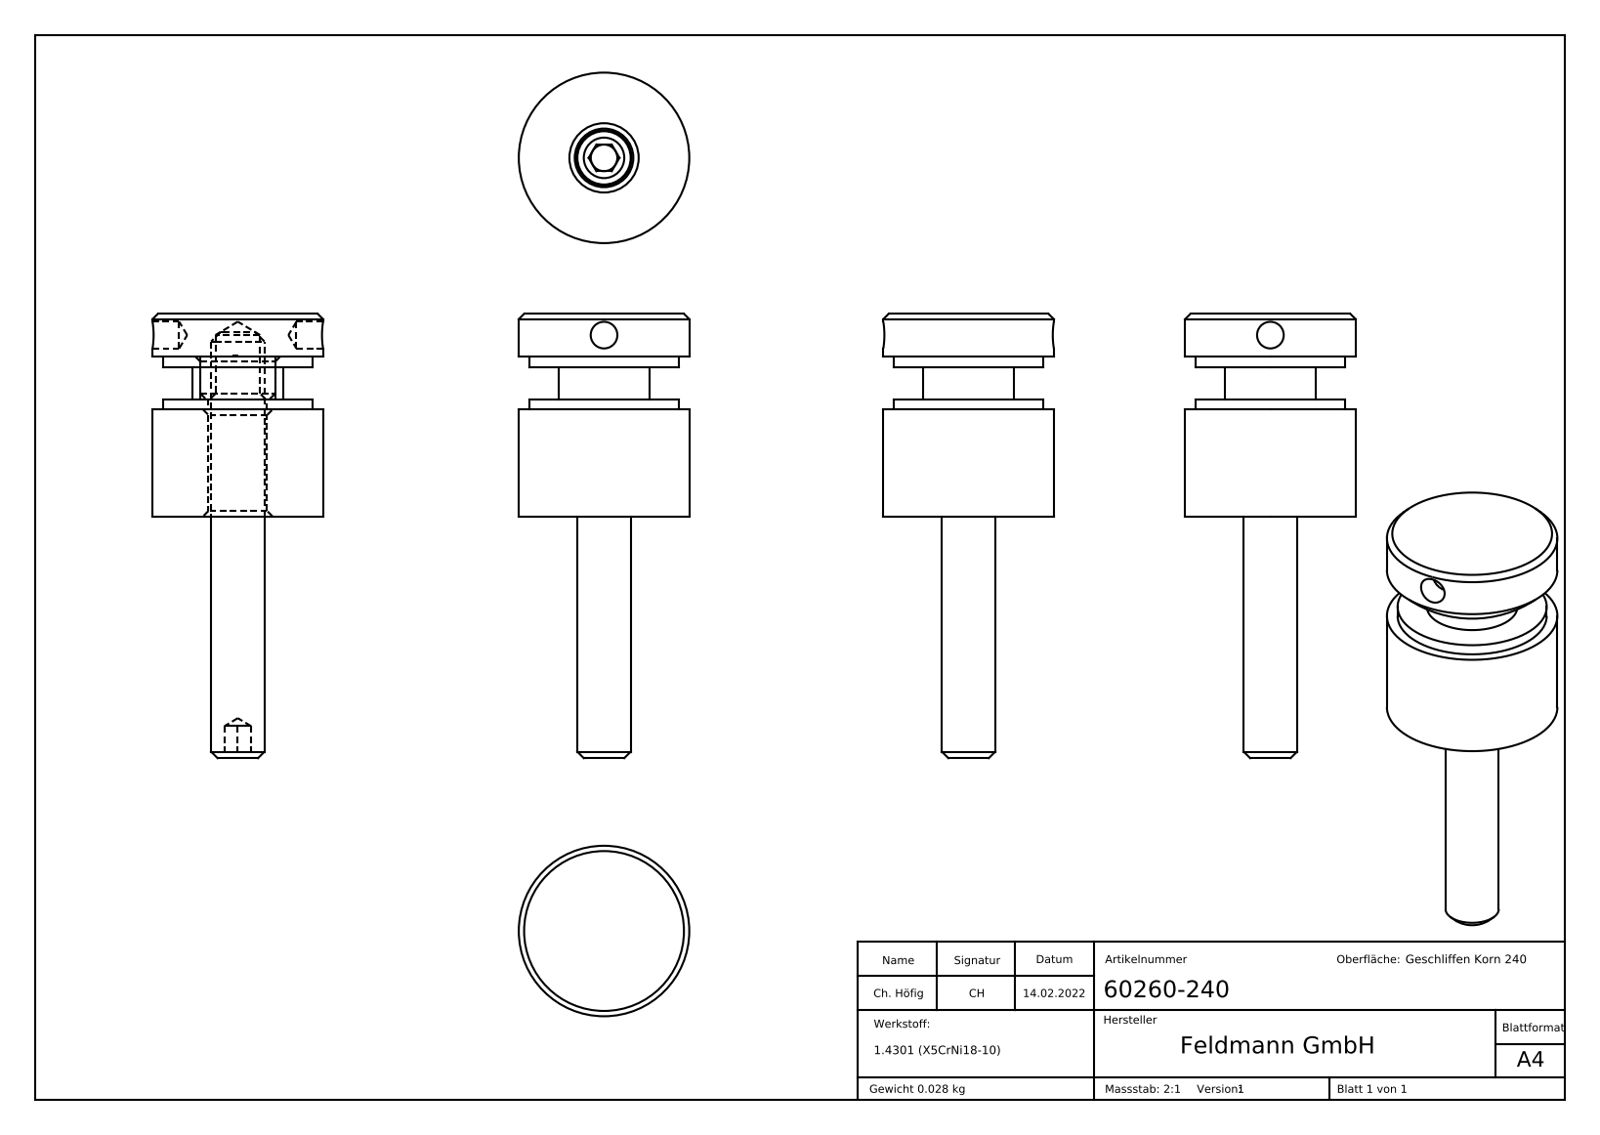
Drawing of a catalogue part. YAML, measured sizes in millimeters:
part_name: "60260-240; 60260-240 Teil3; DIN913; 60260-240 Teil4 (+7 more)"
step_written_by: "SolidWorks 2018 (CONFIG_CONTROL_DESIGN)"
units: millimeters
bodies: {solids: 5, faces: 294, planar: 139, cylindrical: 26, other: 129}
overall_size: [70, 16, 16]
volume: 3658
surface_area: 3249
round_holes:
  - {diameter: 2.5, count: 1}
  - {diameter: 4.2, count: 1}
  - {diameter: 5.5, count: 1}
  - {diameter: 7, count: 1}
round_bosses_or_shafts:
  - {diameter: 16, count: 1}
  - {diameter: 14, count: 1}
  - {diameter: 8.5, count: 1}
  - {diameter: 5, count: 1}
face_to_face_distances: [4, 5, 1, 9, 10, 15, 19, 11, 8, 3]
